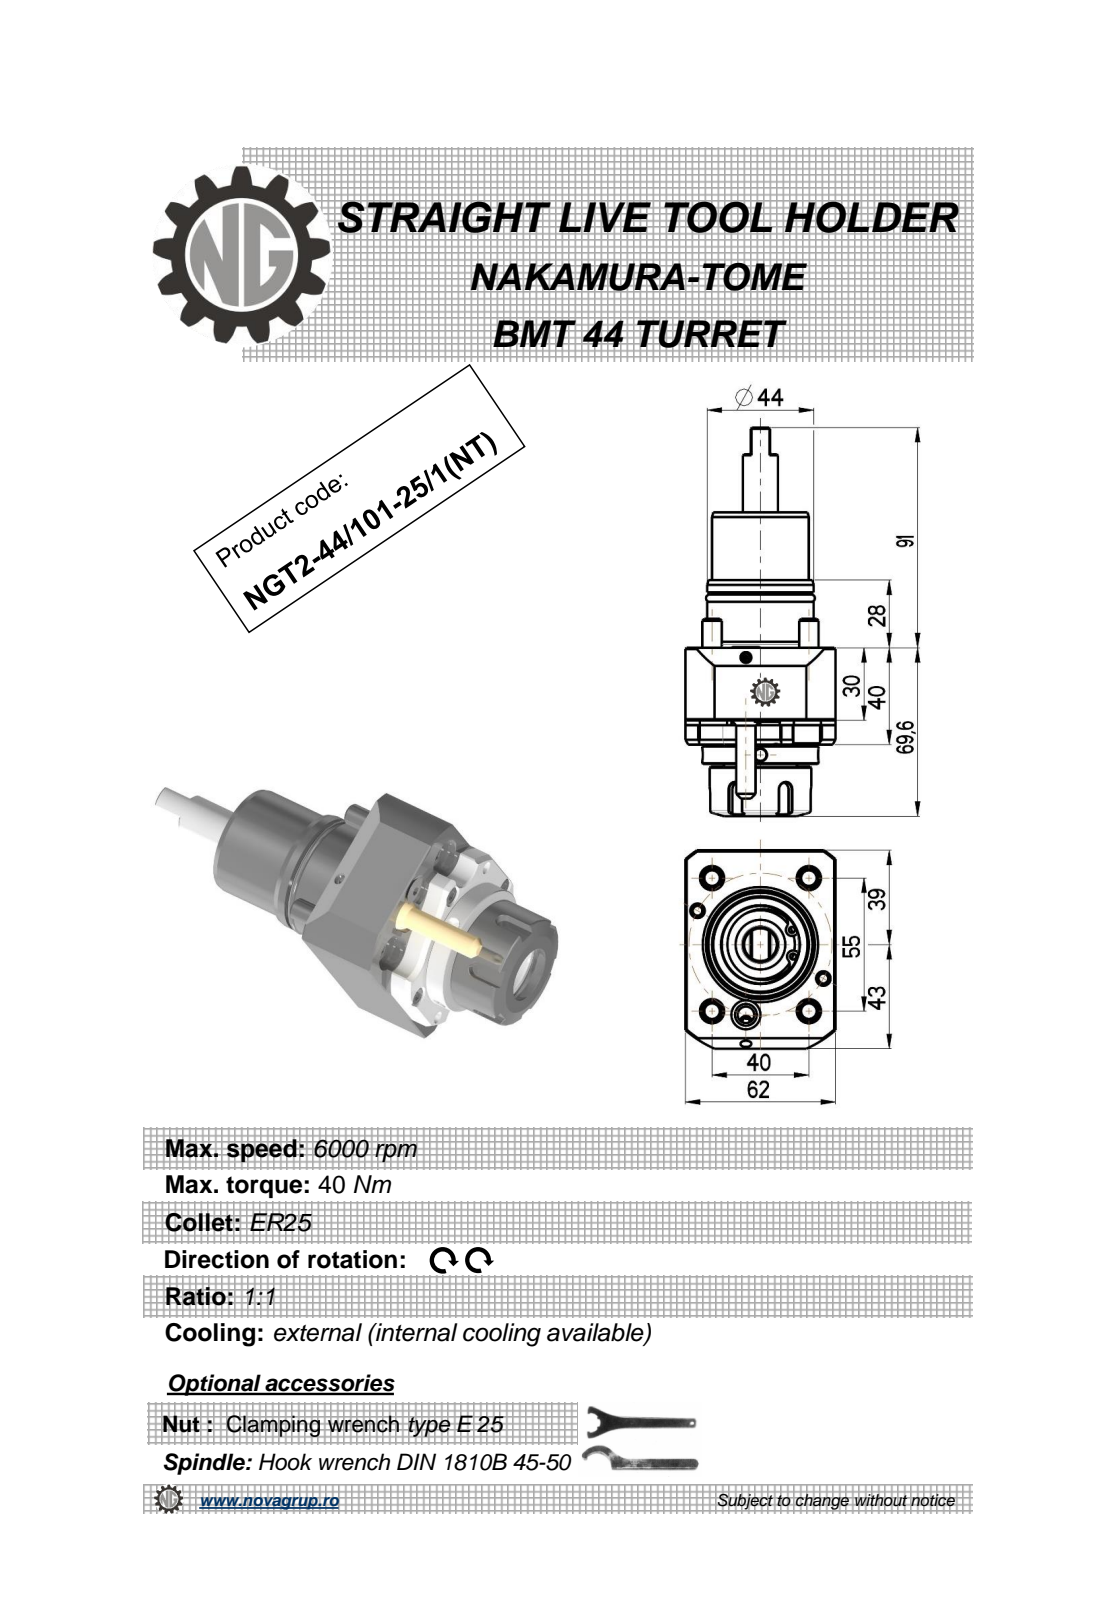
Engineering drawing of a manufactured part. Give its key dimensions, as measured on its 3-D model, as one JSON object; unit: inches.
{"part_name": "NGT2_44_101_25_1_NT", "step_written_by": "PRO/ENGINEER BY PARAMETRIC TECHNOLOGY CORPORATION, 2010280 (CONFIG_CONTROL_DESIGN)", "units": "inches", "bodies": {"solids": 2, "faces": 291, "planar": 93, "cylindrical": 81, "other": 117}, "overall_size": [6.323, 3.228, 2.441], "volume_in3": 18.57, "surface_area_in2": 63.28, "round_holes": [[0.197, 3], [0.118, 1], [0.268, 1], [0.799, 1]], "round_bosses_or_shafts": [[0.315, 5], [1.89, 1], [1.732, 1], [1.709, 1], [1.654, 1], [1.575, 1], [1.535, 1], [1.378, 1]], "partial_cylinders_radius": [[0.009, 6], [0.118, 5], [0.276, 4], [0.031, 2], [0.236, 2], [0.295, 1], [0.995, 1], [1.043, 1]], "face_to_face_distances": [2.441, 1.575, 1.181, 0.394, 3.78, 2.205, 3.386, 0.315, 3.228, 4.094], "hole_center_spacings": [0.118, 1.166, 1.282]}
